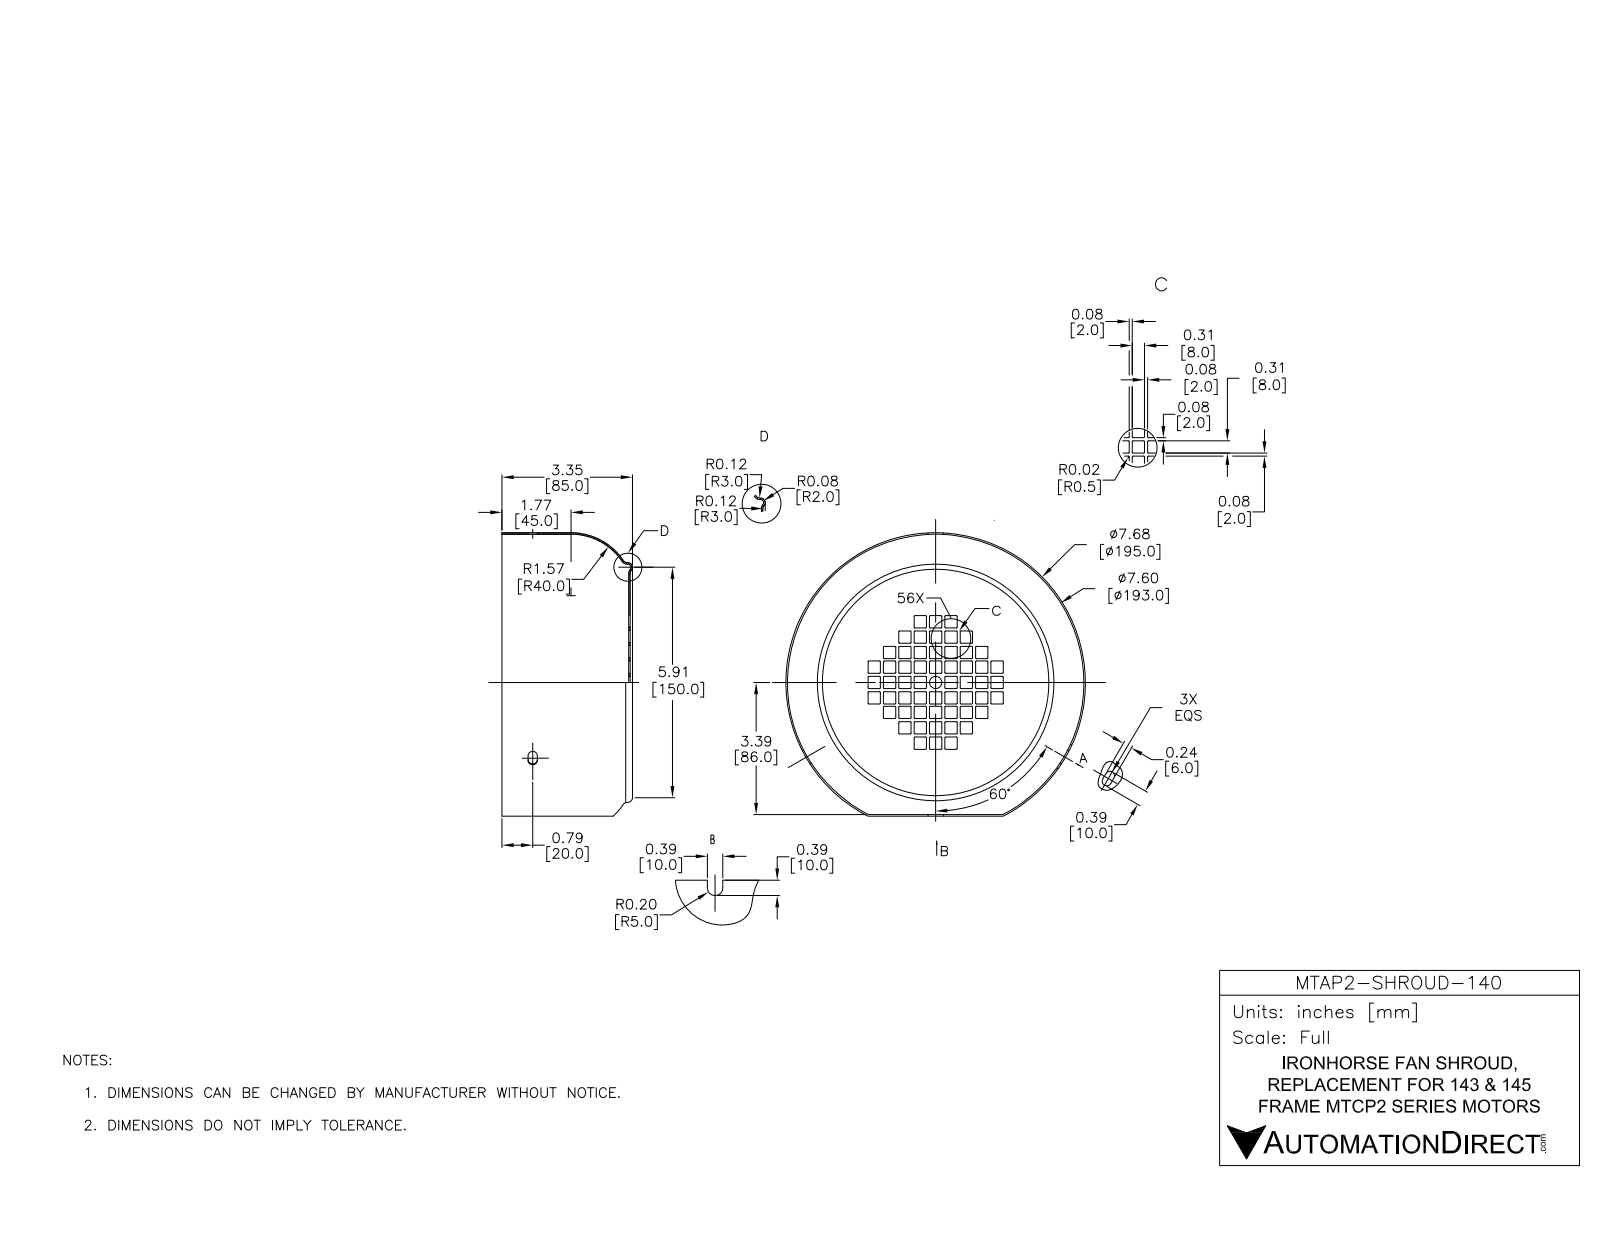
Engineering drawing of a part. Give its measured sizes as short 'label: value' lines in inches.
name: MTAP2-SHROUD-140
written by: SolidWorks 2017 (AUTOMOTIVE_DESIGN)
unit: in
bodies: 1 solid, 536 faces (286 planar, 230 cylindrical, 20 other)
size: 7.677 × 7.224 × 3.347
volume: 8.4 in³; area: 223.6 in²
holes: 1× ⌀0.315, 1× ⌀7.52
bosses: 1× ⌀7.677
rounds: 224× R0.02
face distances: 0.079, 0.039, 3.209, 3.248, 3.288, 0.394, 0.787, 1.181, 0.315, 1.575
